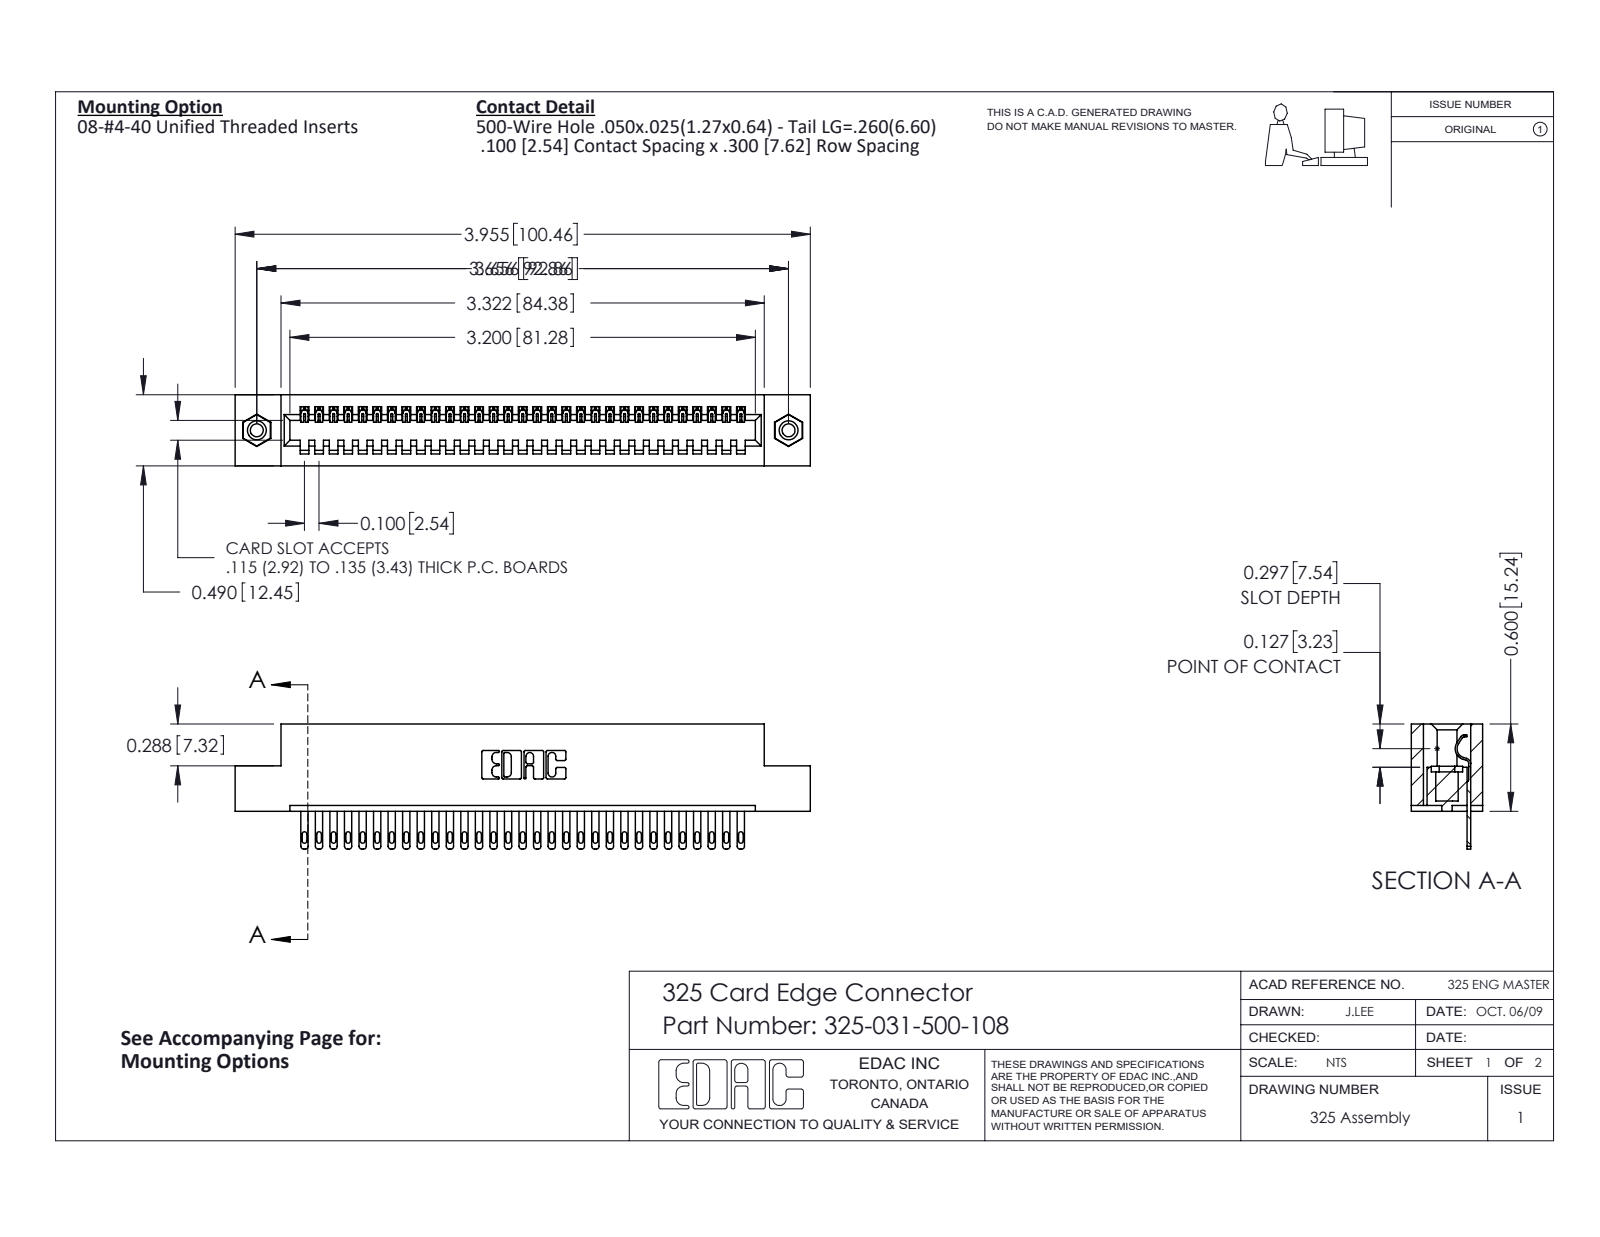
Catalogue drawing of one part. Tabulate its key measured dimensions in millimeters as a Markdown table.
| quantity | value |
| --- | --- |
| part name | 325-031-500-108; 345-250-001_345-250-003-102; 325 Part_TI; 325-292-001_325-293-100 |
| STEP written by | SolidWorks 2016 (CONFIG_CONTROL_DESIGN) |
| units | millimeters |
| bodies | 34 solids, 1848 faces (1218 planar, 614 cylindrical, 16 other) |
| overall size | 100.5 × 21.8 × 12.4 |
| volume | 12 700 mm³ |
| surface area | 13 750 mm² |
| round holes (diameter × count) | 2.3 × 2, 3.2 × 2, 4.1 × 2 |
| round bosses / shafts (diameter × count) | 3.9 × 2 |
| partial cylindrical surfaces (radius × count) | 0.2 × 62, 0.4 × 62, 0.5 × 62, 0.3 × 22, 0.2 × 6, 0.8 × 6, 0.7 × 3, 0.4 × 1 |
| main face-to-face distances | 2.1, 10.3, 7.6, 12.4, 2.7, 9.7, 0.6, 8.3, 1, 2.5 |
| hole center spacings | 92.9 |
